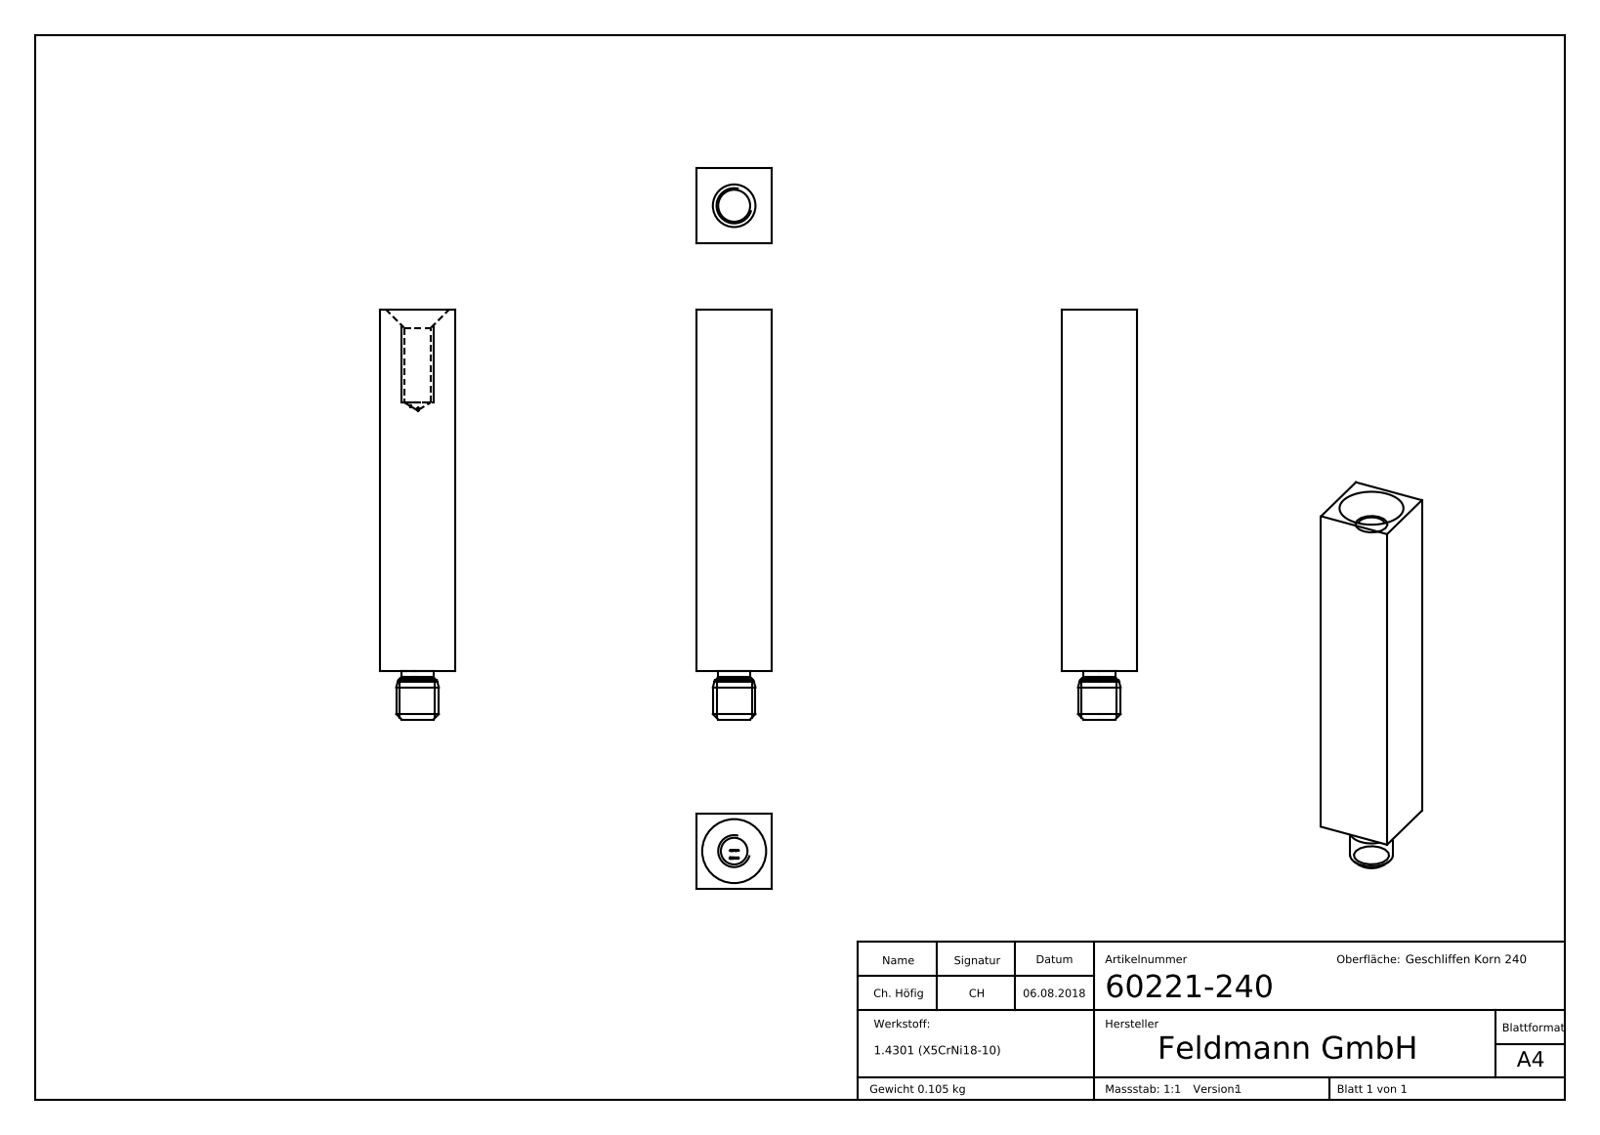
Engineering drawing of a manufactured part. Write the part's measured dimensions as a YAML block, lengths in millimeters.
part_name: "60221-240"
step_written_by: "SolidWorks 2015 (CONFIG_CONTROL_DESIGN)"
units: millimeters
bodies: {solids: 1, faces: 247, planar: 105, cylindrical: 6, other: 136}
overall_size: [77, 14, 14]
volume: 13235
surface_area: 4692
round_holes:
  - {diameter: 5, count: 1}
round_bosses_or_shafts:
  - {diameter: 8, count: 1}
  - {diameter: 6, count: 1}
face_to_face_distances: [14, 68, 9, 77, 8.44, 5.56, 0.48, 1.46, 1.44, 7]
